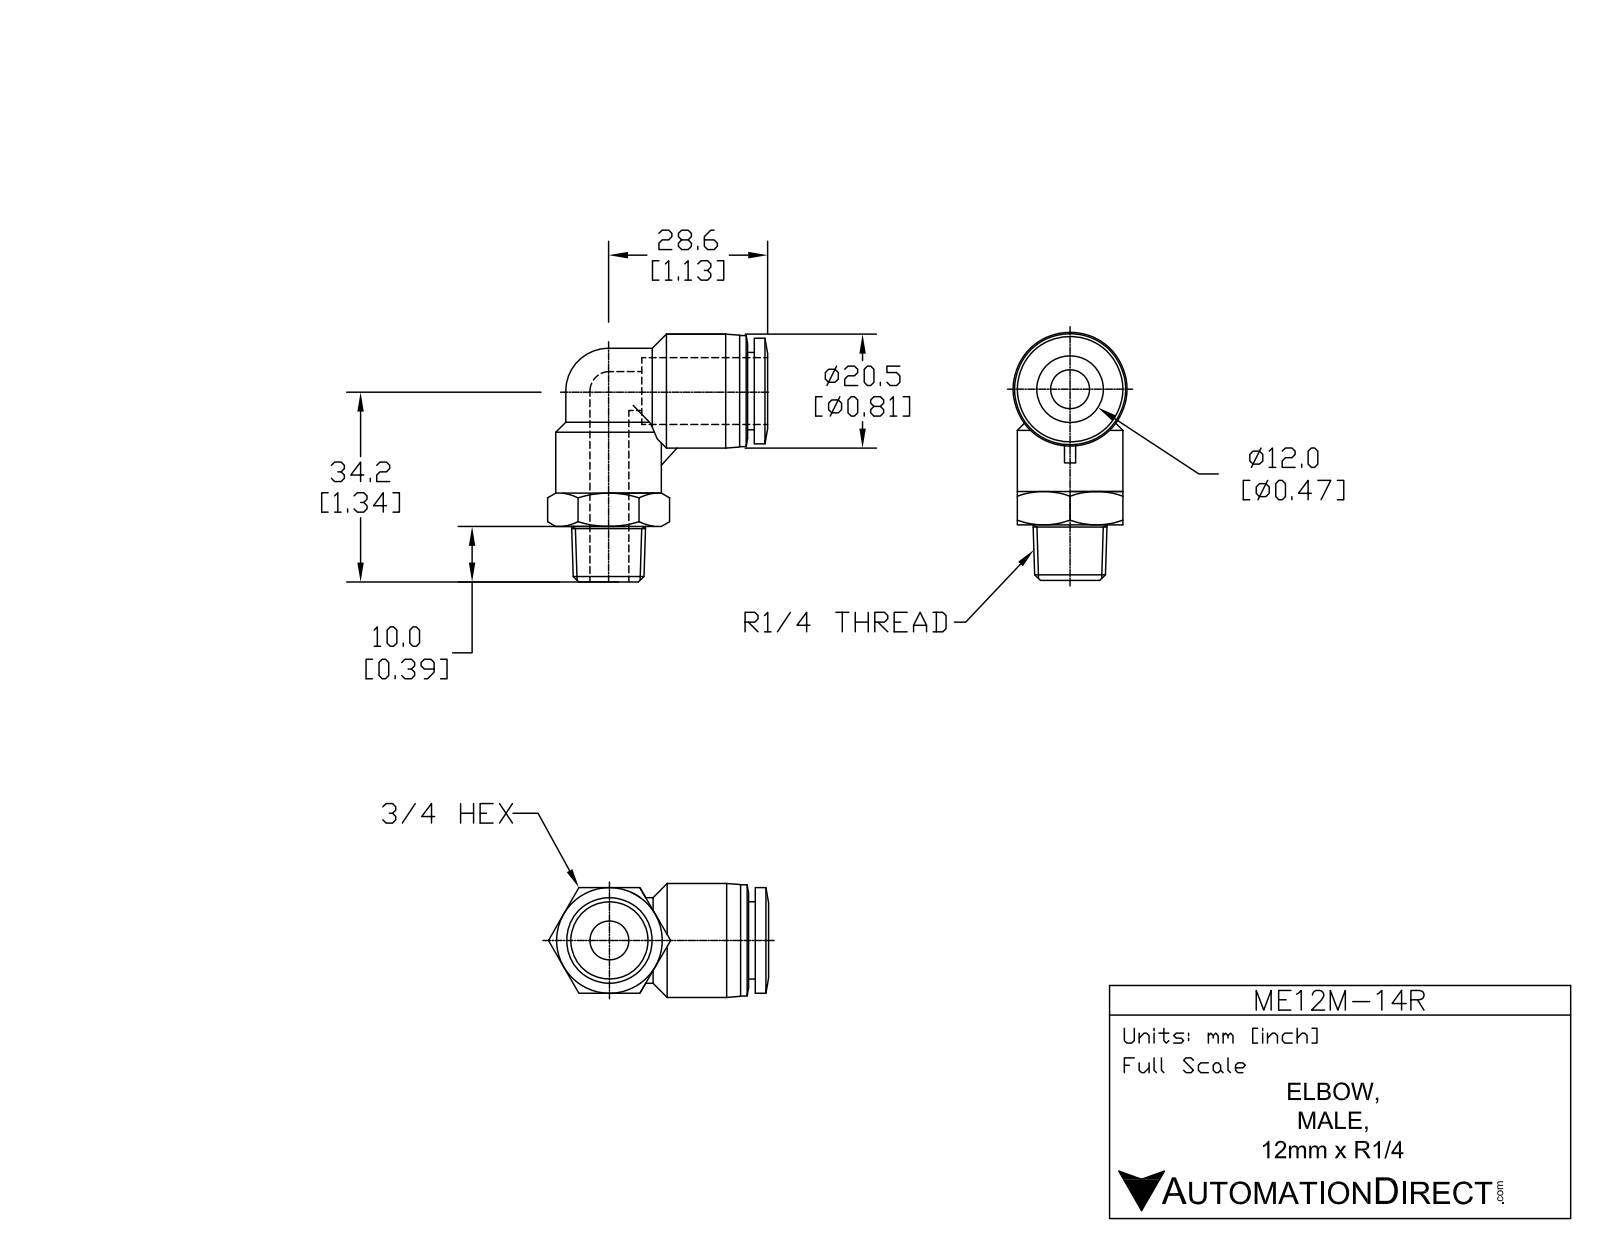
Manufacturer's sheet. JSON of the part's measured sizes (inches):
{"part_name": "ME12M-14R", "step_written_by": "SolidWorks 2015 (AUTOMOTIVE_DESIGN)", "units": "inches", "bodies": {"solids": 1, "faces": 66, "planar": 16, "cylindrical": 19, "other": 31}, "overall_size": [1.758, 1.56, 0.807], "volume_in3": 0.615, "surface_area_in2": 9.587, "round_holes": [[0.354, 2], [0.484, 1]], "round_bosses_or_shafts": [[0.748, 2], [0.807, 1], [0.787, 1], [0.606, 1], [0.547, 1]], "partial_cylinders_radius": [[0.303, 1]], "face_to_face_distances": [0.748, 0.047, 0.76, 0.807, 0.394, 0.902, 0.142, 0.094, 0.335, 0.413]}
